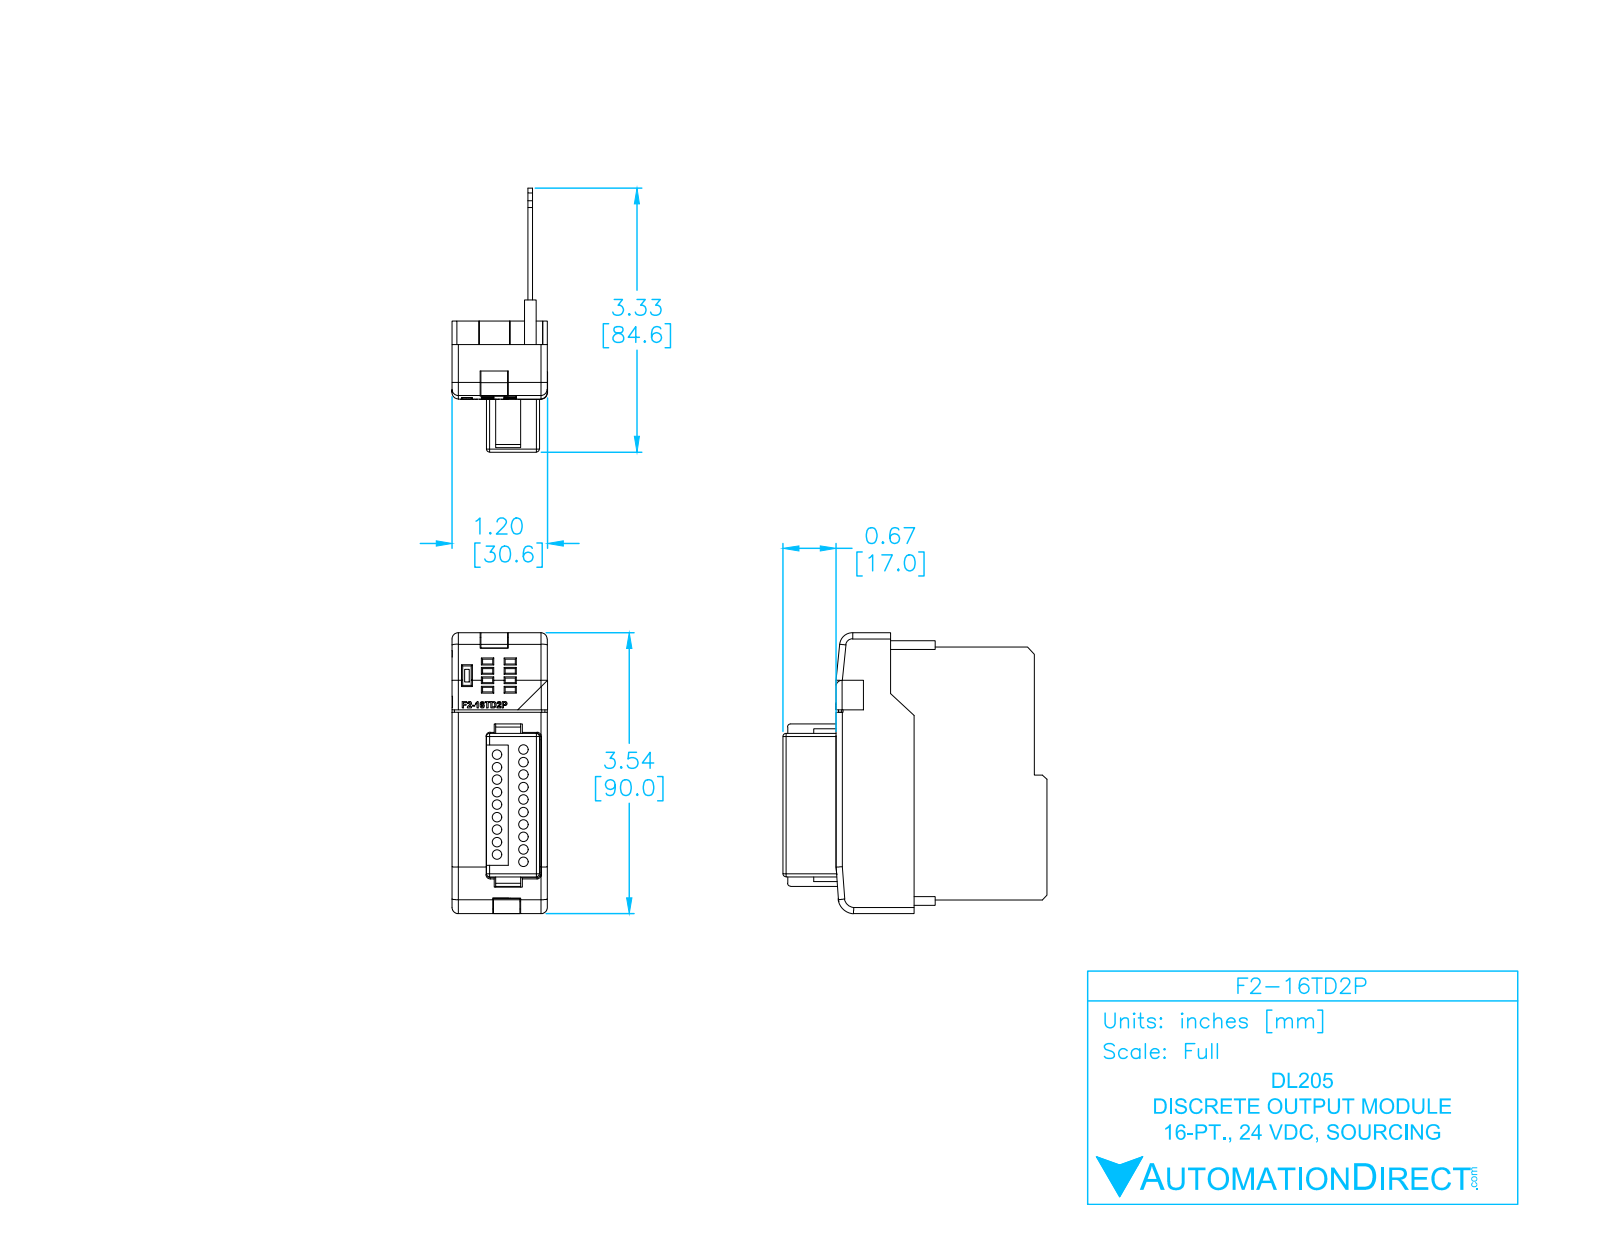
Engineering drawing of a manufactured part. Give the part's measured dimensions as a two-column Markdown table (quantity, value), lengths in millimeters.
| quantity | value |
| --- | --- |
| part name | F2-16TD2P |
| STEP written by | SolidWorks 2009 (AUTOMOTIVE_DESIGN) |
| units | millimeters |
| bodies | 2 solids, 644 faces (418 planar, 158 cylindrical, 68 other) |
| overall size | 90 × 84.6 × 30.55 |
| volume | 30 556 mm³ |
| surface area | 32 609 mm² |
| round holes (diameter × count) | 3 × 19 |
| partial cylindrical surfaces (radius × count) | 0.35 × 28, 1 × 18, 0.5 × 12, 2 × 11, 0.25 × 6, 2.62 × 1, 3.79 × 1, 4.12 × 1 |
| main face-to-face distances | 1.5, 4.72, 3.22, 6.22, 0.5, 1, 24.28, 29, 18, 11 |
| hole center spacings | 4, 8, 12, 16, 8.61, 8.77, 20, 10.16 |
